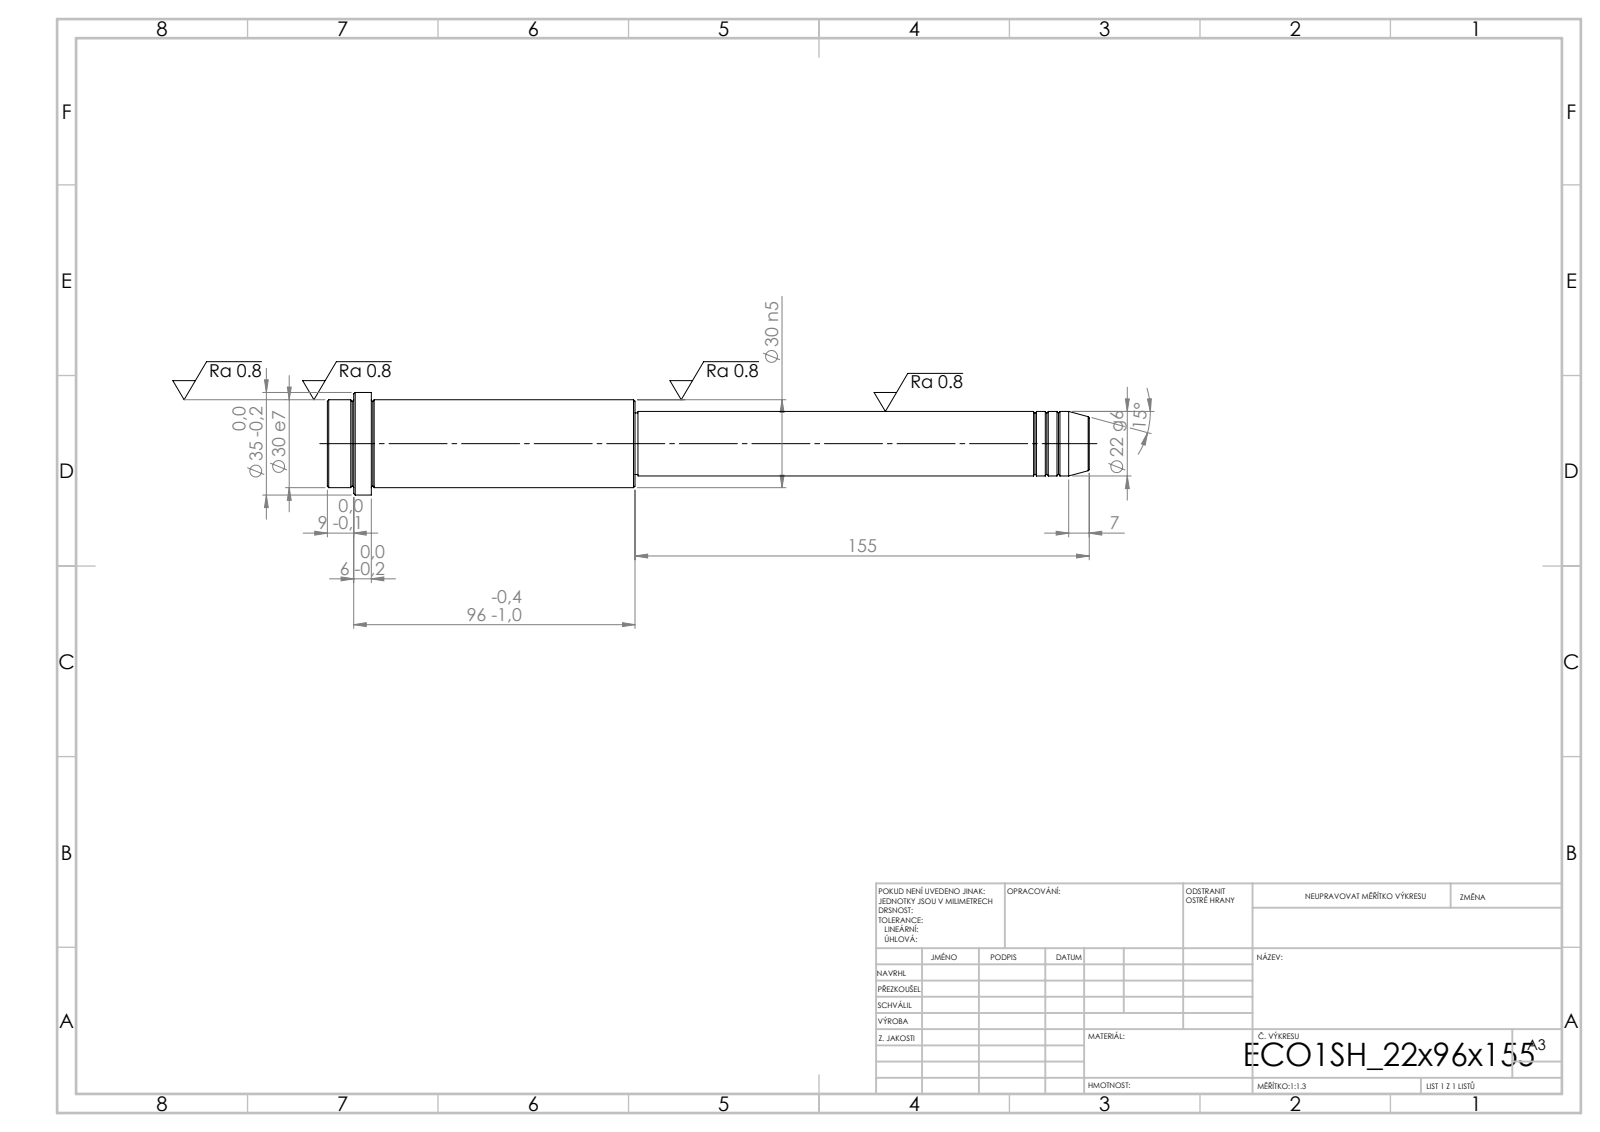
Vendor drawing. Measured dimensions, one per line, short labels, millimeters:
written by: SolidWorks 2019 (CONFIG_CONTROL_DESIGN)
unit: mm
bodies: 1 solid, 52 faces (6 planar, 16 cylindrical, 30 other)
size: 260 × 35 × 35
volume: 134 019 mm³; area: 22 663 mm²
bosses: 1× ⌀35, 1× ⌀30, 1× ⌀22, 1× ⌀21
face distances: 105, 90, 15, 155, 245, 260, 251, 96, 6, 9
